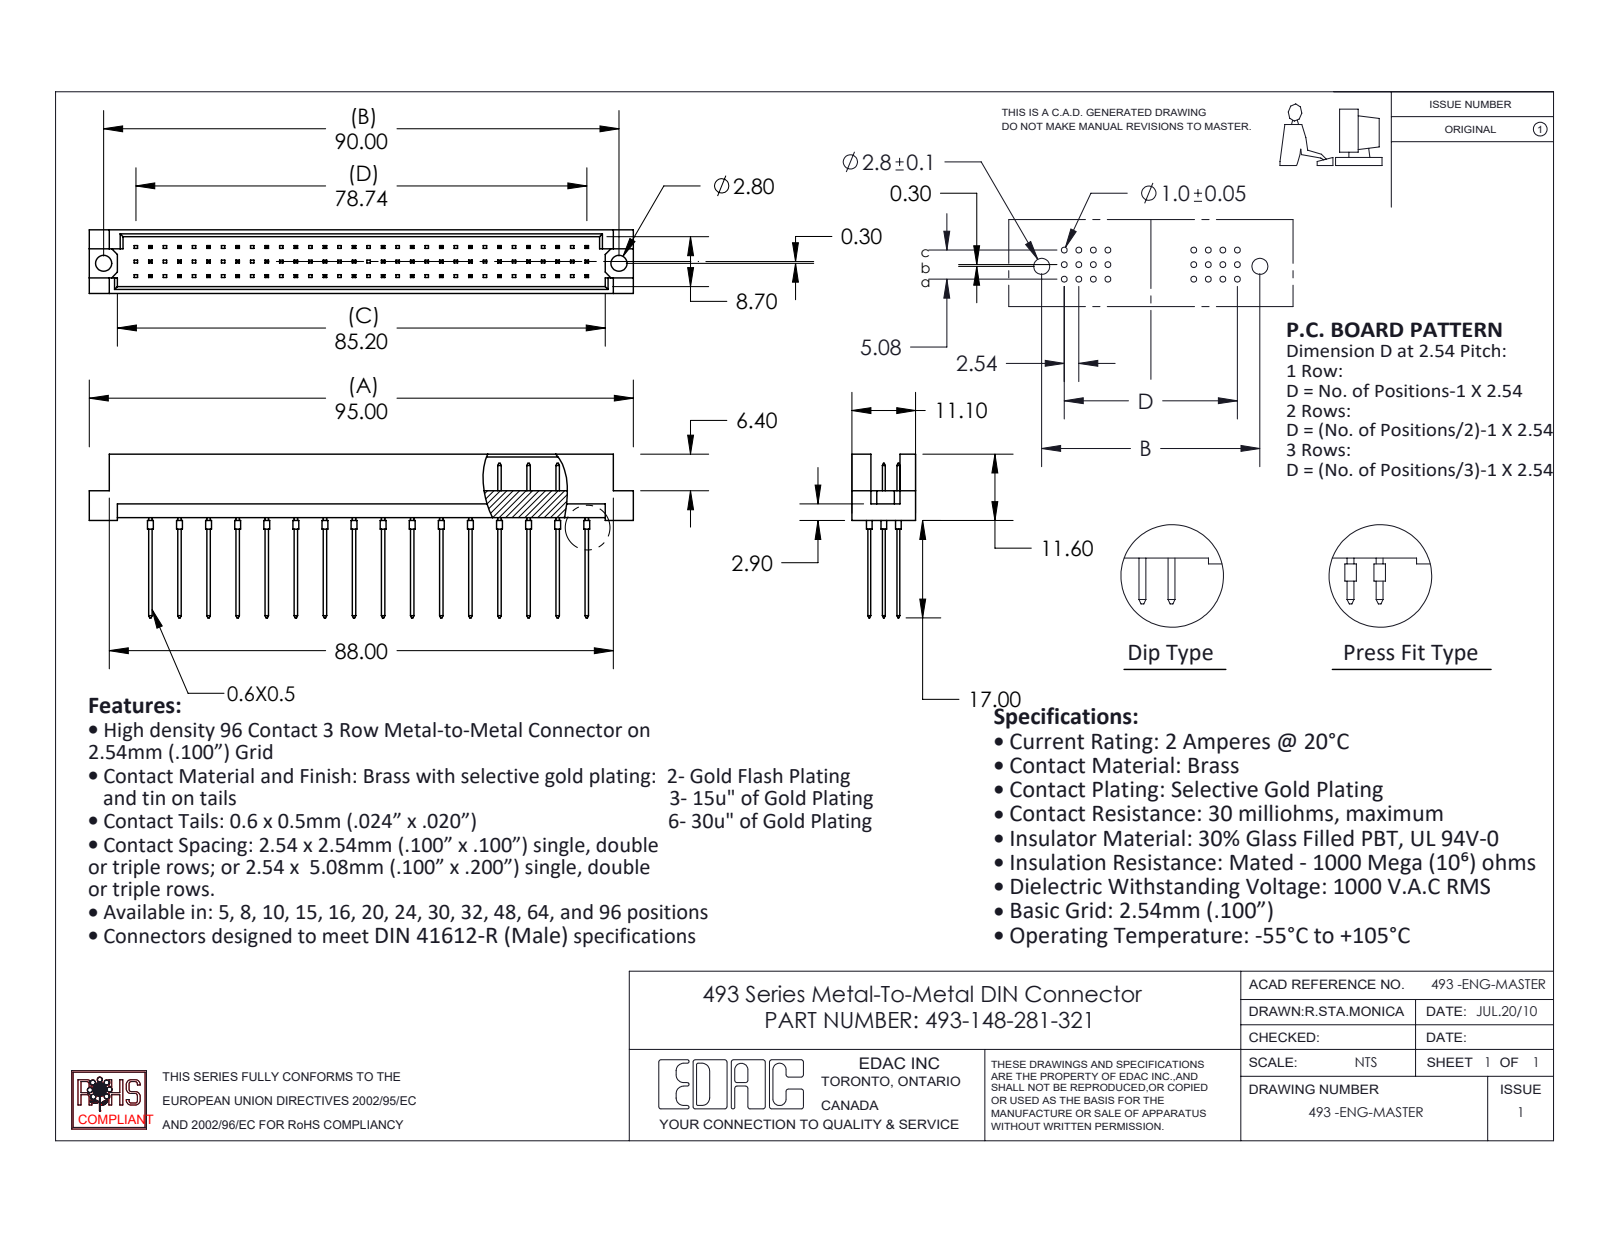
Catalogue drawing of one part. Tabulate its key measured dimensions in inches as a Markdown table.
| quantity | value |
| --- | --- |
| part name | 493-148-281-321; 493 Part_96; 493-290_81 |
| STEP written by | SolidWorks 2020 (CONFIG_CONTROL_DESIGN) |
| units | inches |
| bodies | 49 solids, 1492 faces (1392 planar, 100 cylindrical, 0 other) |
| overall size | 3.74 × 1.126 × 0.437 |
| volume | 0.371 in³ |
| surface area | 14.6 in² |
| round holes (diameter × count) | 0.11 × 2 |
| round bosses / shafts (diameter × count) | 0.039 × 48 |
| main face-to-face distances | 0.047, 0.39, 0.2, 0.1, 0.02, 0.437, 0.343, 0.185, 0.109, 0.128 |
| hole center spacings | 3.543 |
